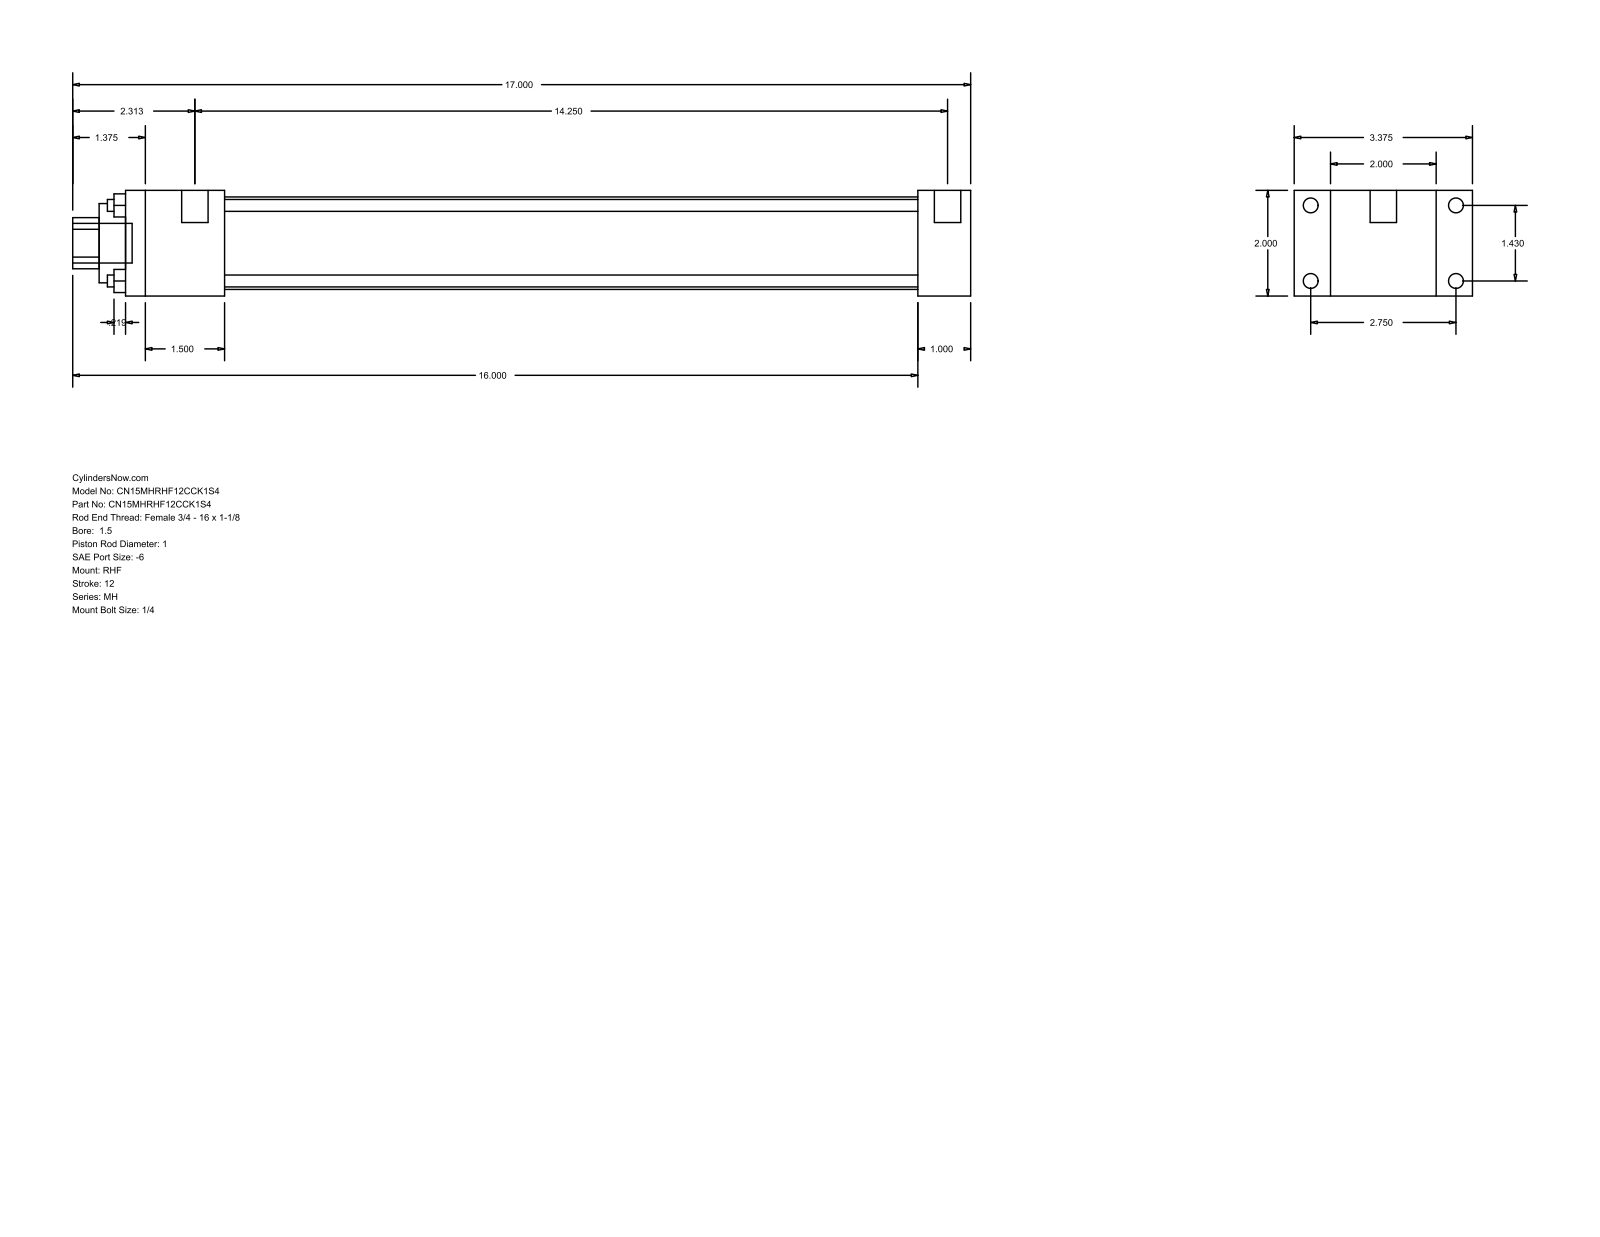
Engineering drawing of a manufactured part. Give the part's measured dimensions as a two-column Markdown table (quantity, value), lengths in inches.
| quantity | value |
| --- | --- |
| part name | MH_RHF__0150_1 |
| STEP written by | GSSL Pune (CONFIG_CONTROL_DESIGN) |
| units | inches |
| bodies | 0 solids, 88 faces (60 planar, 28 cylindrical, 0 other) |
| overall size | 17 × 3.375 × 2 |
| round holes (diameter × count) | 0.225 × 4, 1 × 1, 1.5 × 1, 1.75 × 1 |
| round bosses / shafts (diameter × count) | 0.281 × 4, 0.219 × 4, 0.5 × 2, 0.75 × 1 |
| partial cylindrical surfaces (radius × count) | 0.484 × 1 |
| main face-to-face distances | 2, 1, 0.687, 2.687, 3.375, 16, 15, 1.875, 13.125, 14.125 |
| hole center spacings | 1.011, 1.43, 2.022 |
